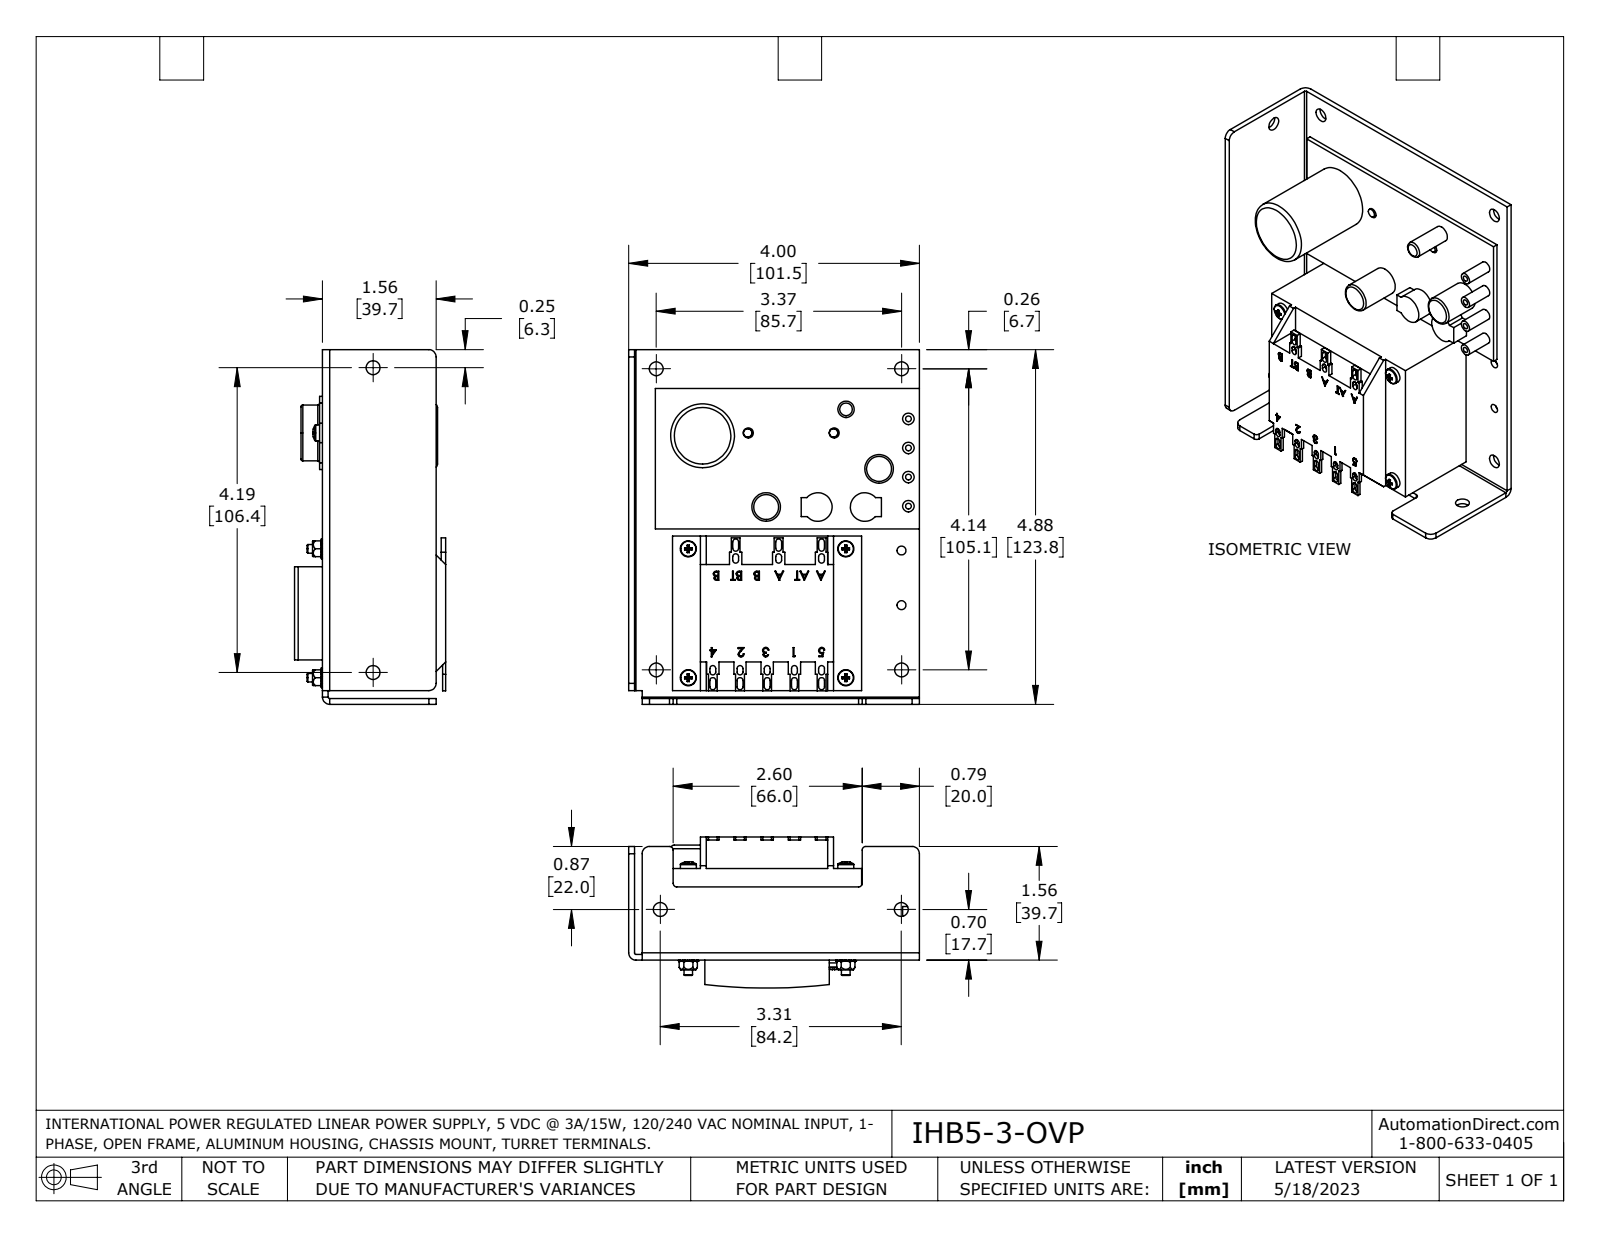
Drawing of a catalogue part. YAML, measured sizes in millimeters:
part_name: "IHB5-3-OVP"
step_written_by: "SolidWorks 2021 (AUTOMOTIVE_DESIGN)"
units: millimeters
bodies: {solids: 2, faces: 948, planar: 635, cylindrical: 208, other: 105}
overall_size: [123.8, 101.5, 52.8]
volume: 203900
surface_area: 70770
round_holes:
  - {diameter: 4.9, count: 8}
  - {diameter: 3, count: 6}
  - {diameter: 2, count: 4}
  - {diameter: 3.3, count: 4}
  - {diameter: 3.1, count: 2}
  - {diameter: 3.5, count: 2}
round_bosses_or_shafts:
  - {diameter: 5.6, count: 6}
  - {diameter: 3, count: 6}
  - {diameter: 4, count: 4}
  - {diameter: 10, count: 2}
  - {diameter: 6.4, count: 2}
  - {diameter: 22.3, count: 1}
  - {diameter: 19.5, count: 1}
  - {diameter: 5.7, count: 1}
partial_cylinders:
  - {radius: 1, count: 32}
  - {radius: 2.5, count: 10}
  - {radius: 1.3, count: 4}
  - {radius: 3.4, count: 4}
  - {radius: 2.5, count: 3}
  - {radius: 0.5, count: 2}
  - {radius: 4.1, count: 2}
  - {radius: 5, count: 2}
face_to_face_distances: [2, 5, 7, 8.7, 6.7, 1.7, 2, 4.8, 2.8, 58.8]
hole_center_spacings: [10.2, 20.3, 30, 45, 55, 71.1, 85.7, 105.1]
